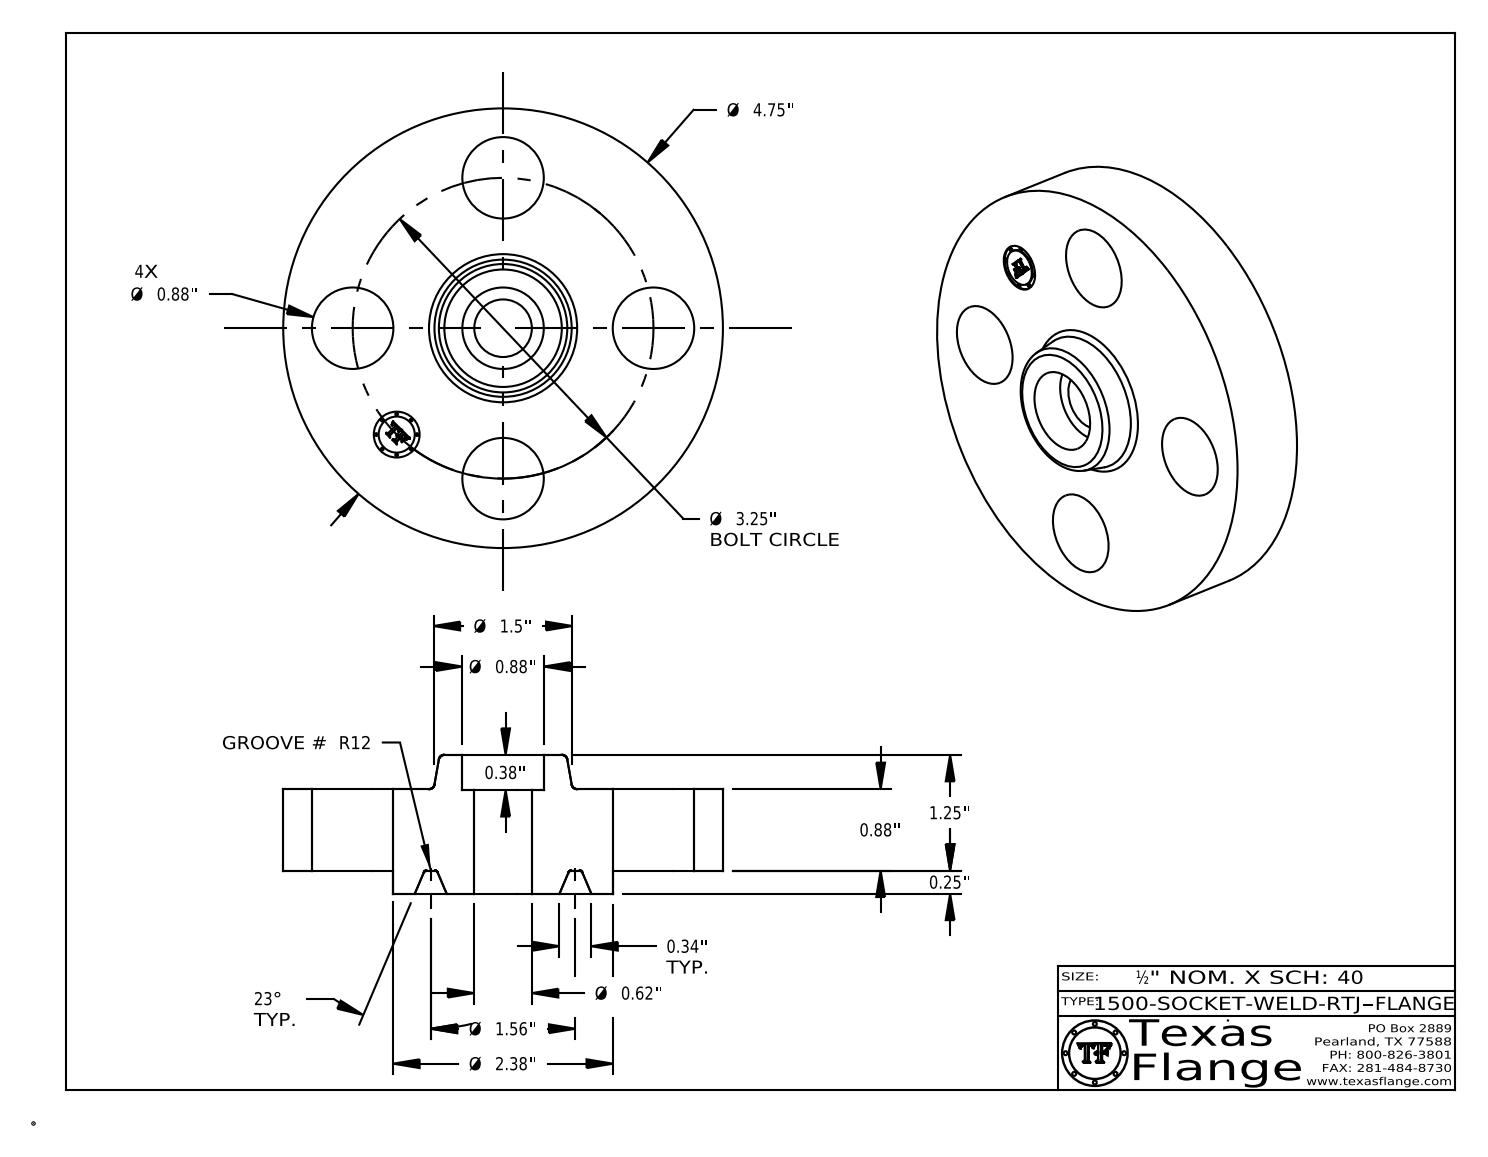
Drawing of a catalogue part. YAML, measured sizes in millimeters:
part_name: "1500-SOCKET-WELD-RTJ"
step_written_by: "CATIA V5 STEP AP214 (AUTOMOTIVE_DESIGN)"
units: millimeters
bodies: {solids: 1, faces: 426, planar: 372, cylindrical: 40, other: 14}
overall_size: [120.7, 120.7, 38.1]
volume: 234300
surface_area: 39260
round_holes:
  - {diameter: 22.4, count: 5}
  - {diameter: 12.6, count: 1}
  - {diameter: 15.8, count: 1}
round_bosses_or_shafts:
  - {diameter: 0.8, count: 8}
  - {diameter: 120.7, count: 1}
  - {diameter: 60.3, count: 1}
  - {diameter: 9.9, count: 1}
face_to_face_distances: [22.4, 6.4, 28.7, 38.1, 31.8, 9.4, 28.4, 22.1, 9.7, 28.3]
hole_center_spacings: [41.3, 58.4, 31.6, 76.3, 82.6]
